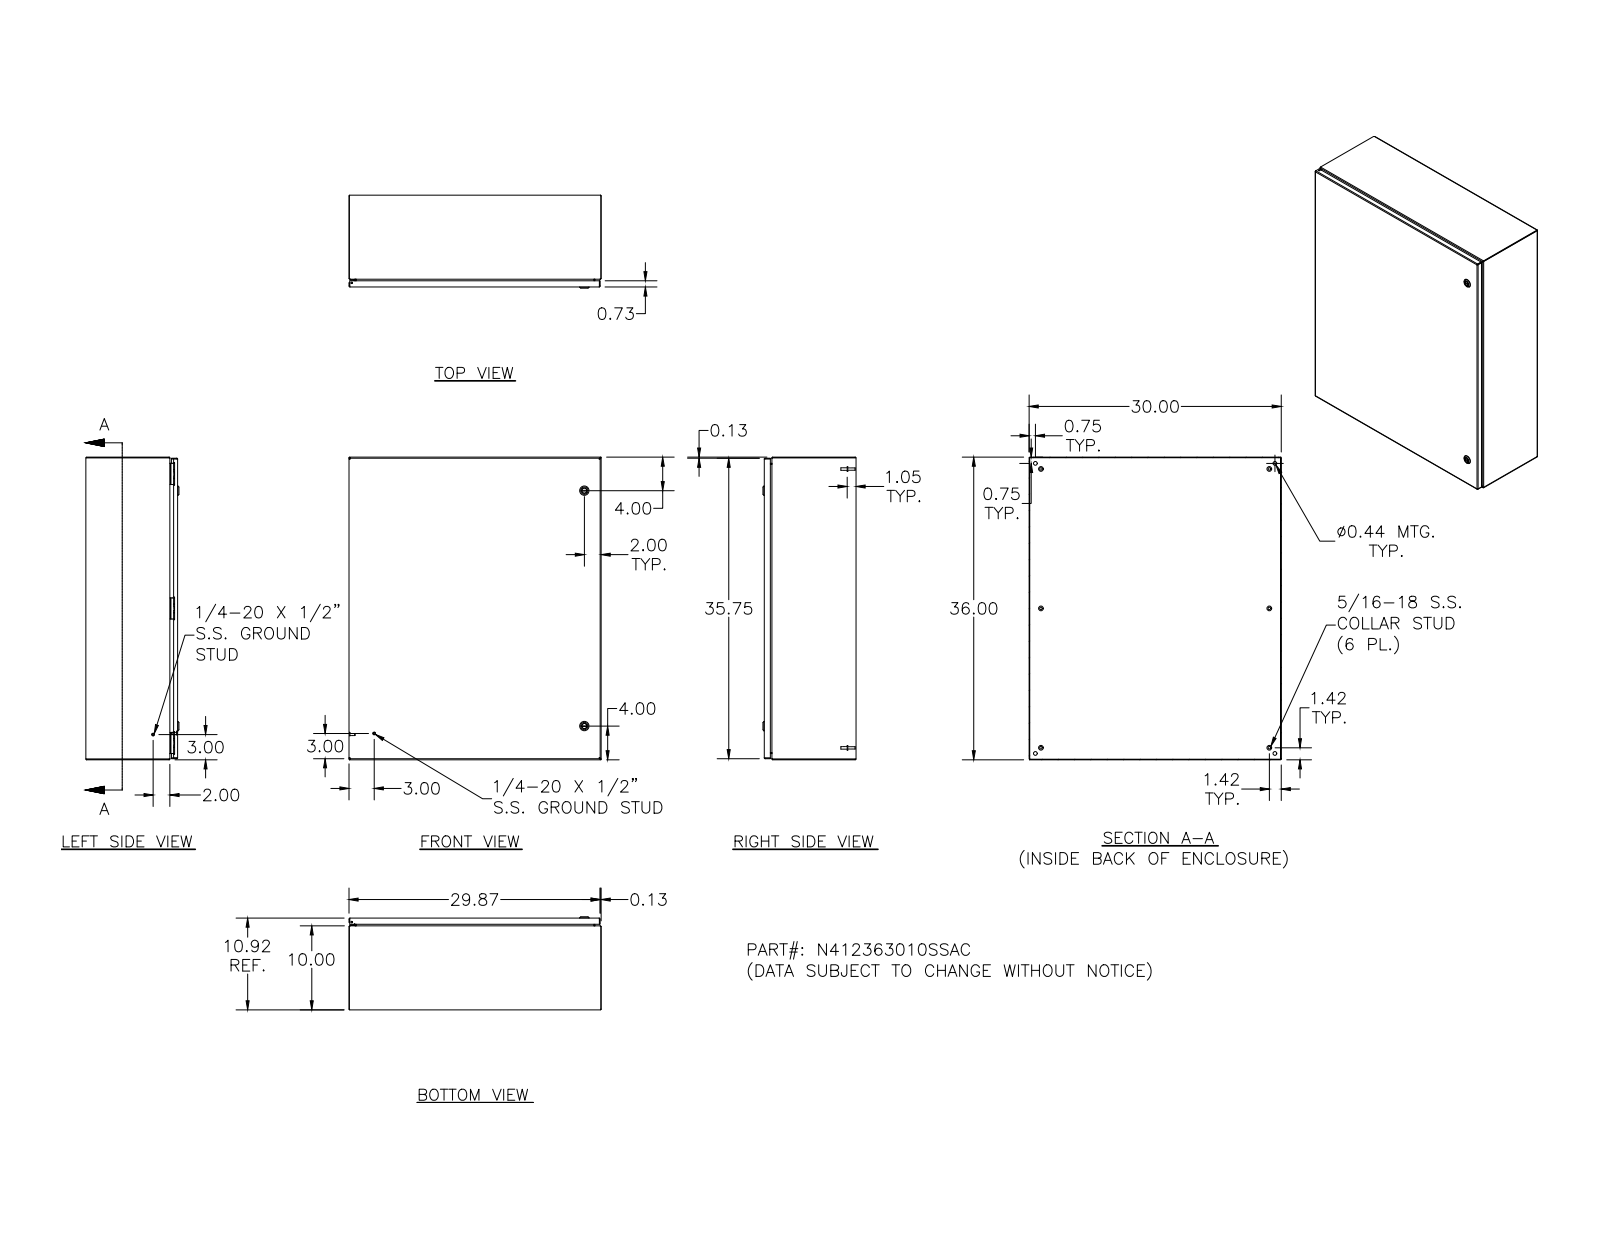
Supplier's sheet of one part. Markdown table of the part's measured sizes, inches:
| quantity | value |
| --- | --- |
| part name | N412363010SSAC; N412363010SSACBKP; 388151; N4123630SSACLID (+8 more) |
| STEP written by | Autodesk Inventor 2011 (AUTOMOTIVE_DESIGN) |
| units | inches |
| bodies | 53 solids, 2098 faces (823 planar, 766 cylindrical, 509 other) |
| overall size | 36 × 30 × 11.075 |
| volume | 278.1 in³ |
| surface area | 7 542 in² |
| round holes (diameter × count) | 0.188 × 7, 0.093 × 6, 0.152 × 6, 0.167 × 6, 0.172 × 6, 0.437 × 4, 0.156 × 3, 0.197 × 2, 0.315 × 2, 0.394 × 2, 0.402 × 2, 0.634 × 2 |
| round bosses / shafts (diameter × count) | 0.25 × 14, 0.563 × 6, 0.36 × 6, 0.32 × 6, 0.3 × 6, 0.275 × 6, 0.256 × 6, 0.164 × 6 |
| partial cylindrical surfaces (radius × count) | 0.05 × 38, 0.016 × 26, 0.125 × 21, 0.031 × 18, 0.016 × 16, 0.09 × 16, 0.02 × 15, 0.032 × 12 |
| main face-to-face distances | 0.074, 10.843, 10.769, 10.917, 29.926, 35.926, 29.852, 30, 36, 35.852 |
| hole center spacings | 16.004, 32, 15.996, 0.017, 0.66, 15.992, 16, 16.008 |
